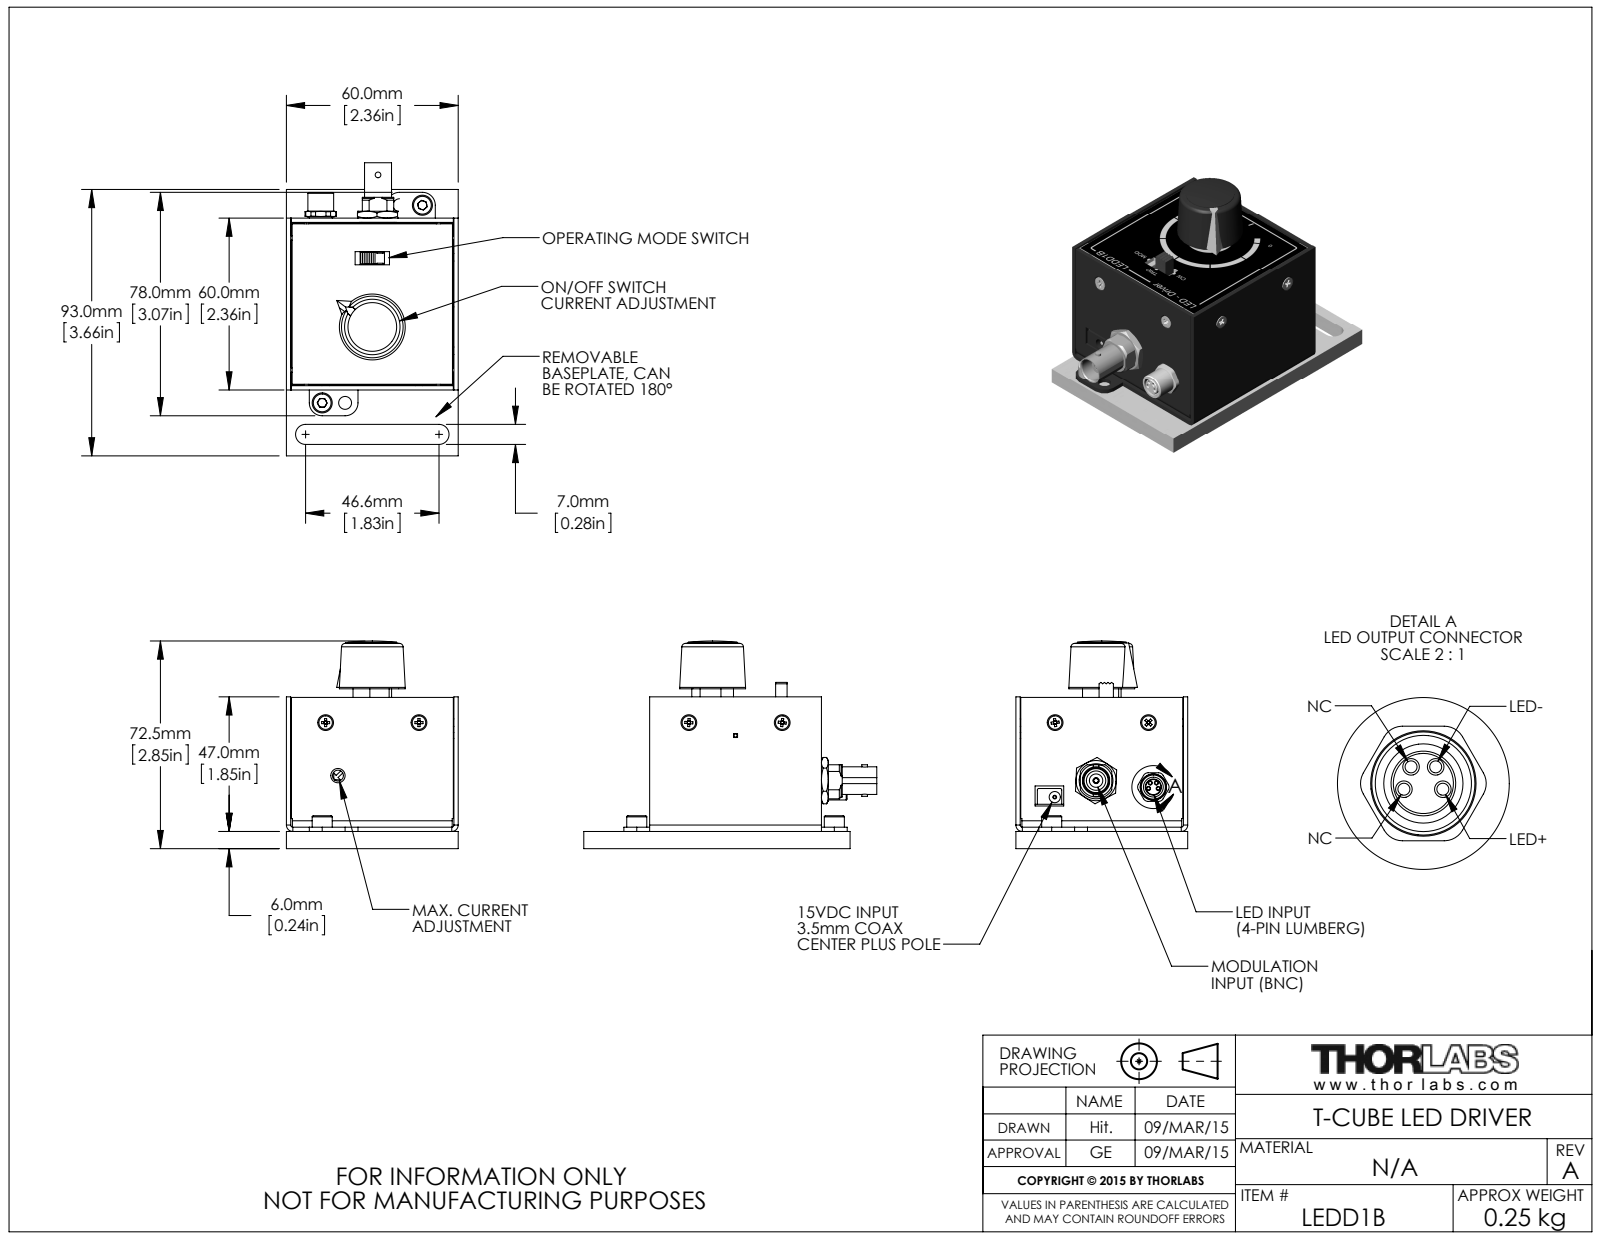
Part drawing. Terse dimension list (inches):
name: MTN003494-E0W
written by: SolidWorks 2014 (AUTOMOTIVE_DESIGN)
unit: in
bodies: 44 solids, 3729 faces (2482 planar, 635 cylindrical, 612 other)
size: 4.029 × 2.854 × 2.362
volume: 4.882 in³; area: 127.1 in²
holes: 10× ⌀0.098, 10× ⌀0.106, 8× ⌀0.081, 8× ⌀0.169, 6× ⌀0.047, 4× ⌀0.041, 4× ⌀0.063, 4× ⌀0.064, 4× ⌀0.079, 4× ⌀0.165, 3× ⌀0.031, 3× ⌀0.051
bosses: 9× ⌀0.039, 8× ⌀0.248, 8× ⌀0.166, 8× ⌀0.141, 4× ⌀0.185, 4× ⌀0.028, 2× ⌀0.276, 2× ⌀0.157
rounds: 26× R0.012, 24× R0.02, 18× R0.016, 8× R0.039, 8× R0.04, 7× R0.029, 6× R0.03, 6× R0.062
face distances: 0.059, 2.303, 1.772, 0.315, 1.457, 0.236, 2.362, 1.831, 2.067, 2.244
hole spacings: 0.134, 0.283, 0.315, 0.467, 0.653, 0.68, 0.729, 0.746
